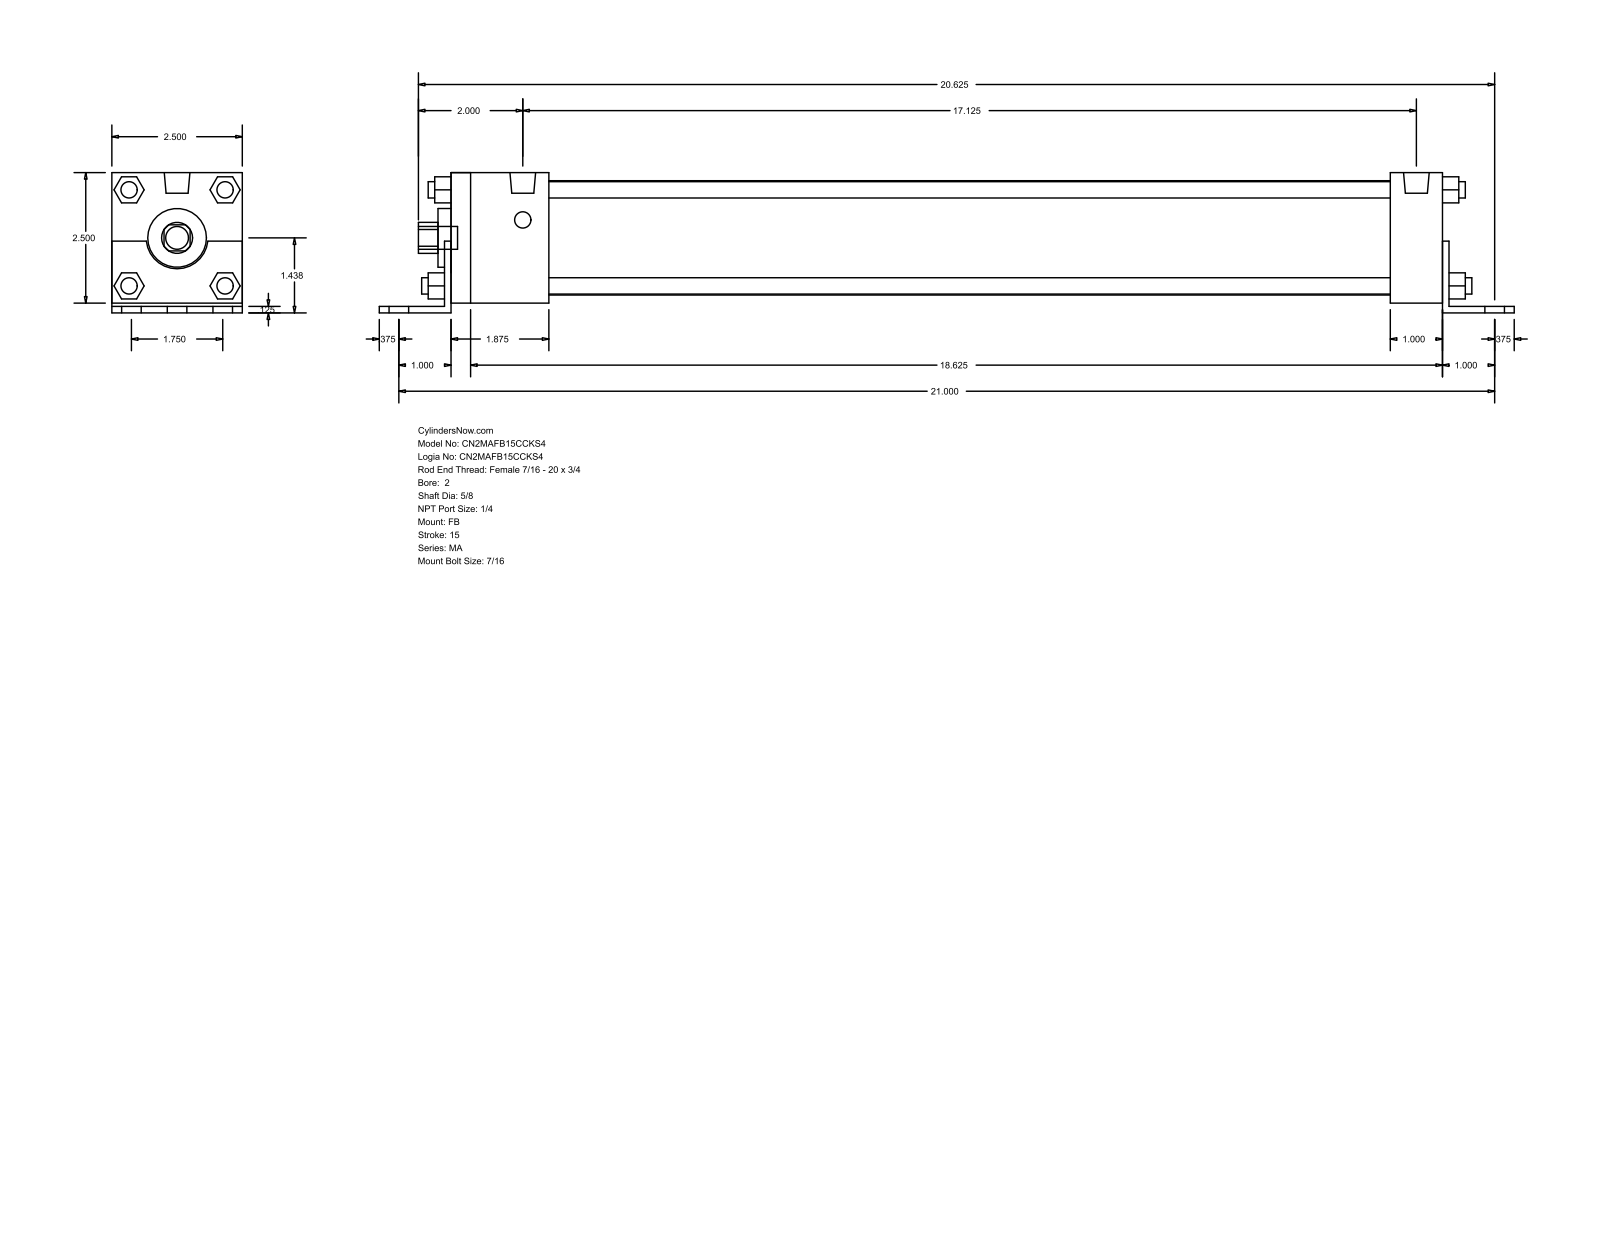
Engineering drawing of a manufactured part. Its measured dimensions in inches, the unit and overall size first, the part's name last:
Units: inches
Overall size (bounding box): 21.75 × 2.687 × 2.5
Round holes (diameter × count): ⌀0.625 ×1, ⌀1.125 ×1, ⌀2.19 ×1
Round bosses / shafts (diameter × count): ⌀0.313 ×8, ⌀0.437 ×7, ⌀0.492 ×2
Partial cylindrical surfaces — rounded edges, fillets, slot ends (radius × count): R0.297 ×1, R0.593 ×1
Main face-to-face distances: 2.5, 0.125, 0.187, 2.687, 0.063, 2.563, 19, 19.25, 0.125, 19.125
Bodies: 0 solids, 140 faces (105 planar, 35 cylindrical, 0 other)
Part name (STEP PRODUCT): MA_FB__0200_0.625
STEP written by: GSSL Pune (CONFIG_CONTROL_DESIGN)
